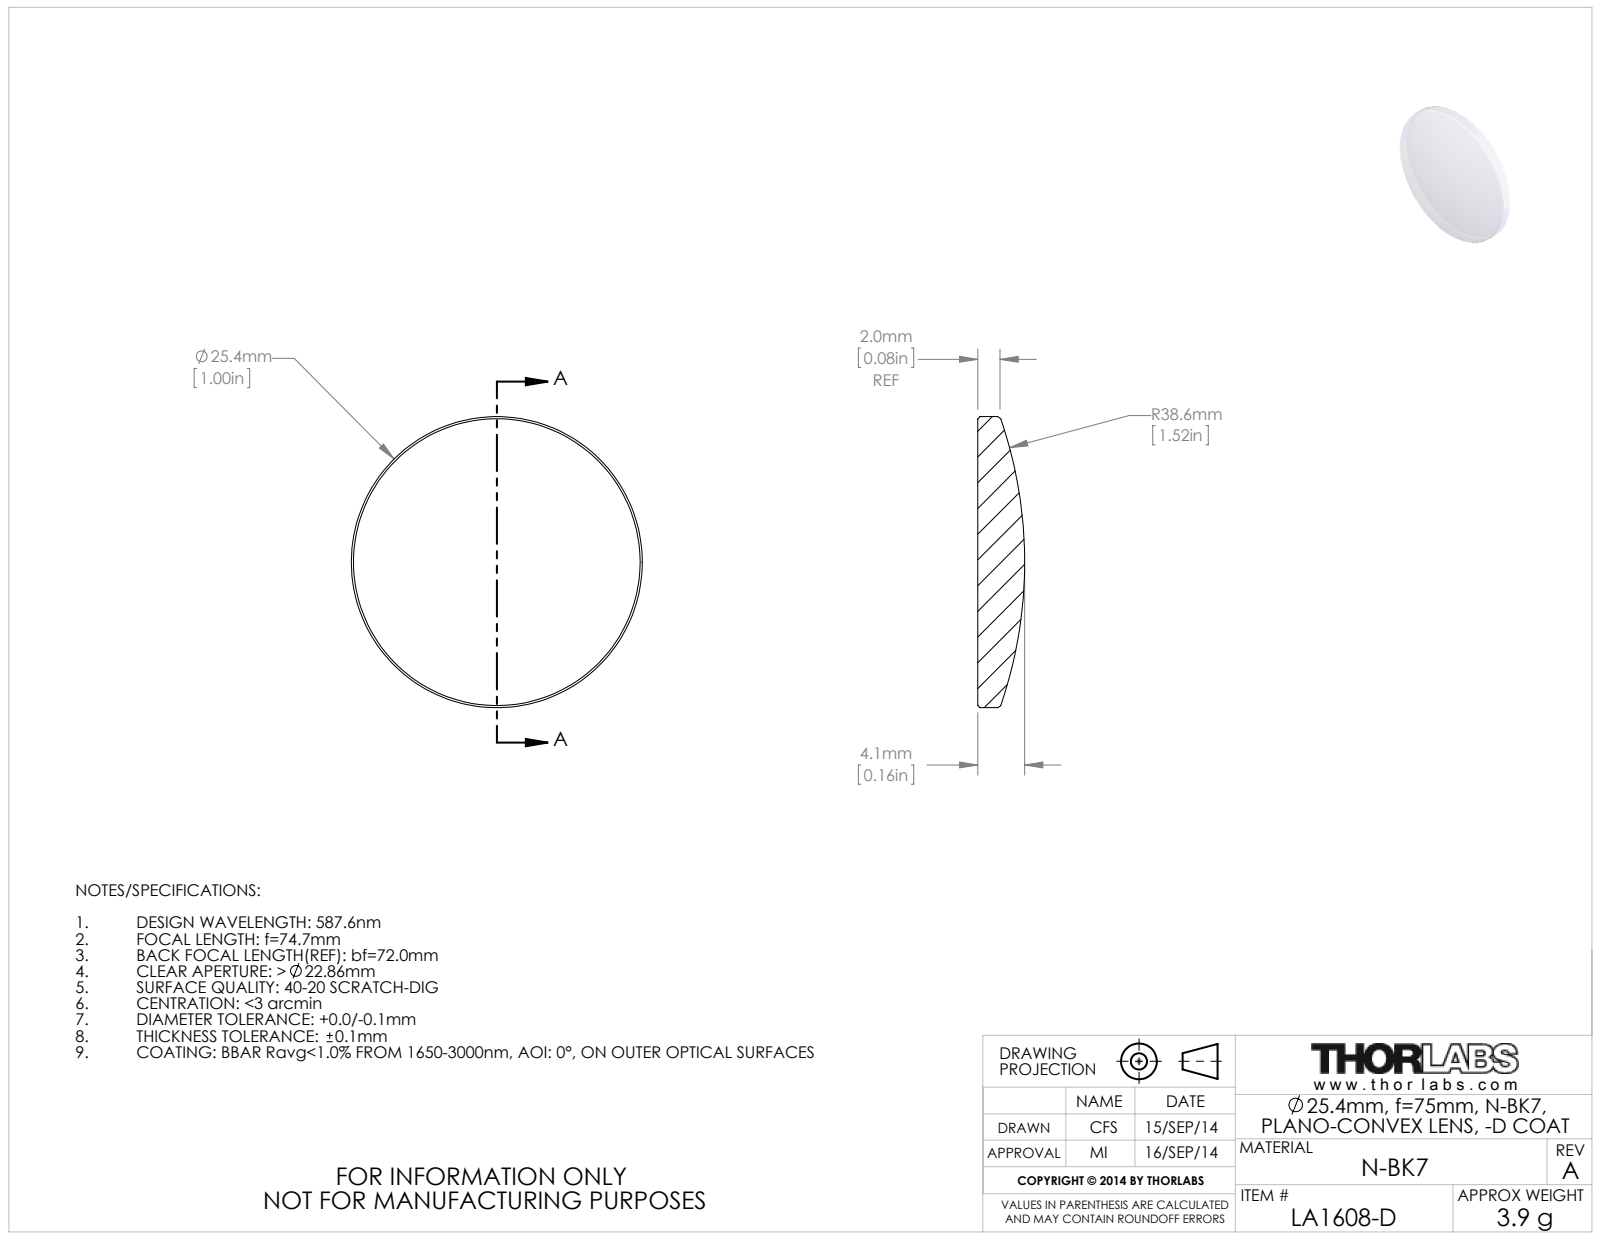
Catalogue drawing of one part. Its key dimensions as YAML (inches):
part_name: "TTN031791-E0W"
step_written_by: "SolidWorks 2014 (CONFIG_CONTROL_DESIGN)"
units: inches
bodies: {solids: 1, faces: 9, planar: 1, cylindrical: 2, other: 6}
overall_size: [1, 1, 0.161]
volume: 0.094
surface_area: 1.811
round_bosses_or_shafts:
  - {diameter: 1, count: 1}
